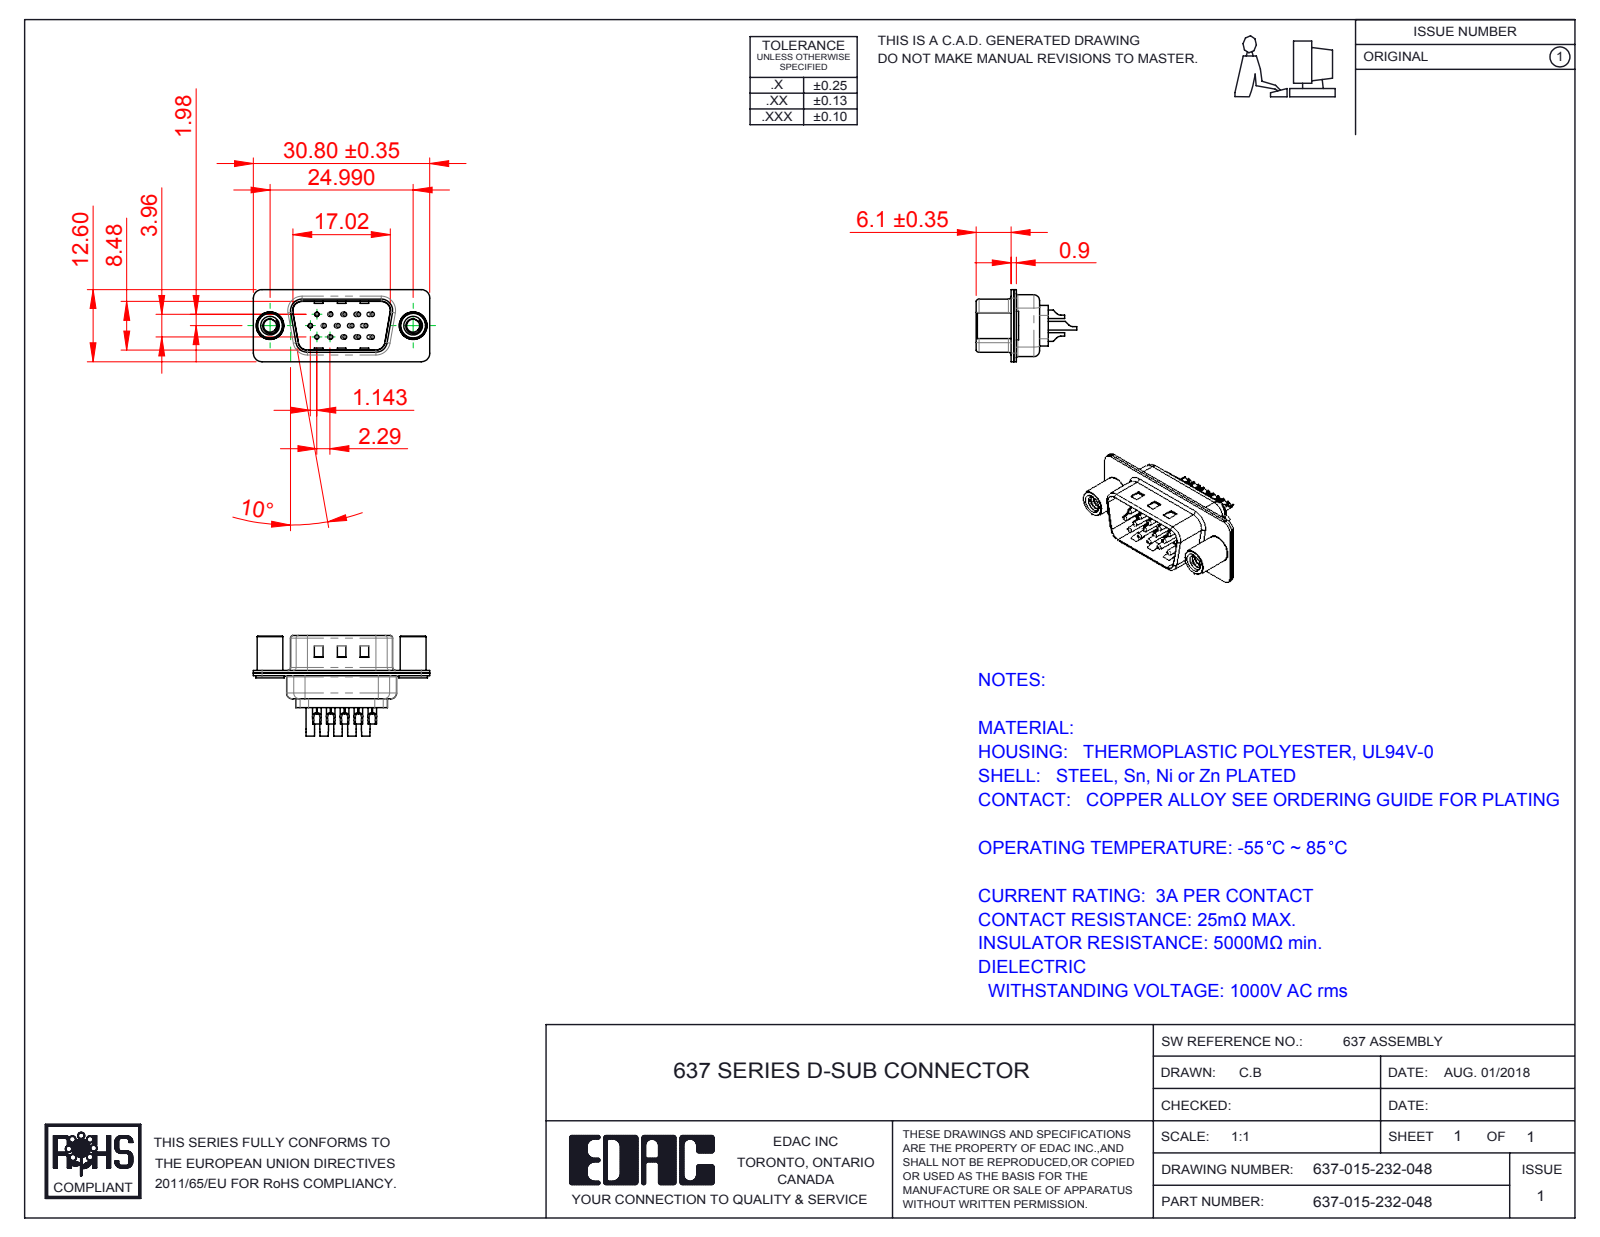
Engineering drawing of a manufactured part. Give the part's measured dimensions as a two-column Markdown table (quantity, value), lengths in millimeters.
| quantity | value |
| --- | --- |
| part name | 637 4-40 Threaded Standoff; 637 Contact Row 3_32; 637 Contact Row 2_32; 637 Contact Row 1_32 (+4 more) |
| STEP written by | SolidWorks 2016 (CONFIG_CONTROL_DESIGN) |
| units | millimeters |
| bodies | 20 solids, 1298 faces (319 planar, 592 cylindrical, 387 other) |
| overall size | 30.8 × 17.55 × 12.6 |
| volume | 1 394 mm³ |
| surface area | 4 972 mm² |
| round holes (diameter × count) | 1.6 × 27, 0.35 × 15, 1.1 × 15, 0.75 × 12, 2 × 12, 2.26 × 2, 4 × 2, 4.8 × 2 |
| round bosses / shafts (diameter × count) | 2 × 15, 1.5 × 15, 0.75 × 15, 5 × 2, 4.9 × 2, 4.5 × 2 |
| partial cylindrical surfaces (radius × count) | 1.5 × 16, 2 × 12, 0.5 × 8, 1 × 7, 0.25 × 4, 0.55 × 4, 0.7 × 4, 0.95 × 4 |
| main face-to-face distances | 0.45, 0.9, 0.4, 0.7, 8.48, 8.88, 0.31, 4.55, 1.05, 1.16 |
| hole center spacings | 3.96, 2.29, 2.28, 4.57, 2.42, 6.05, 4.84, 2.35 |
